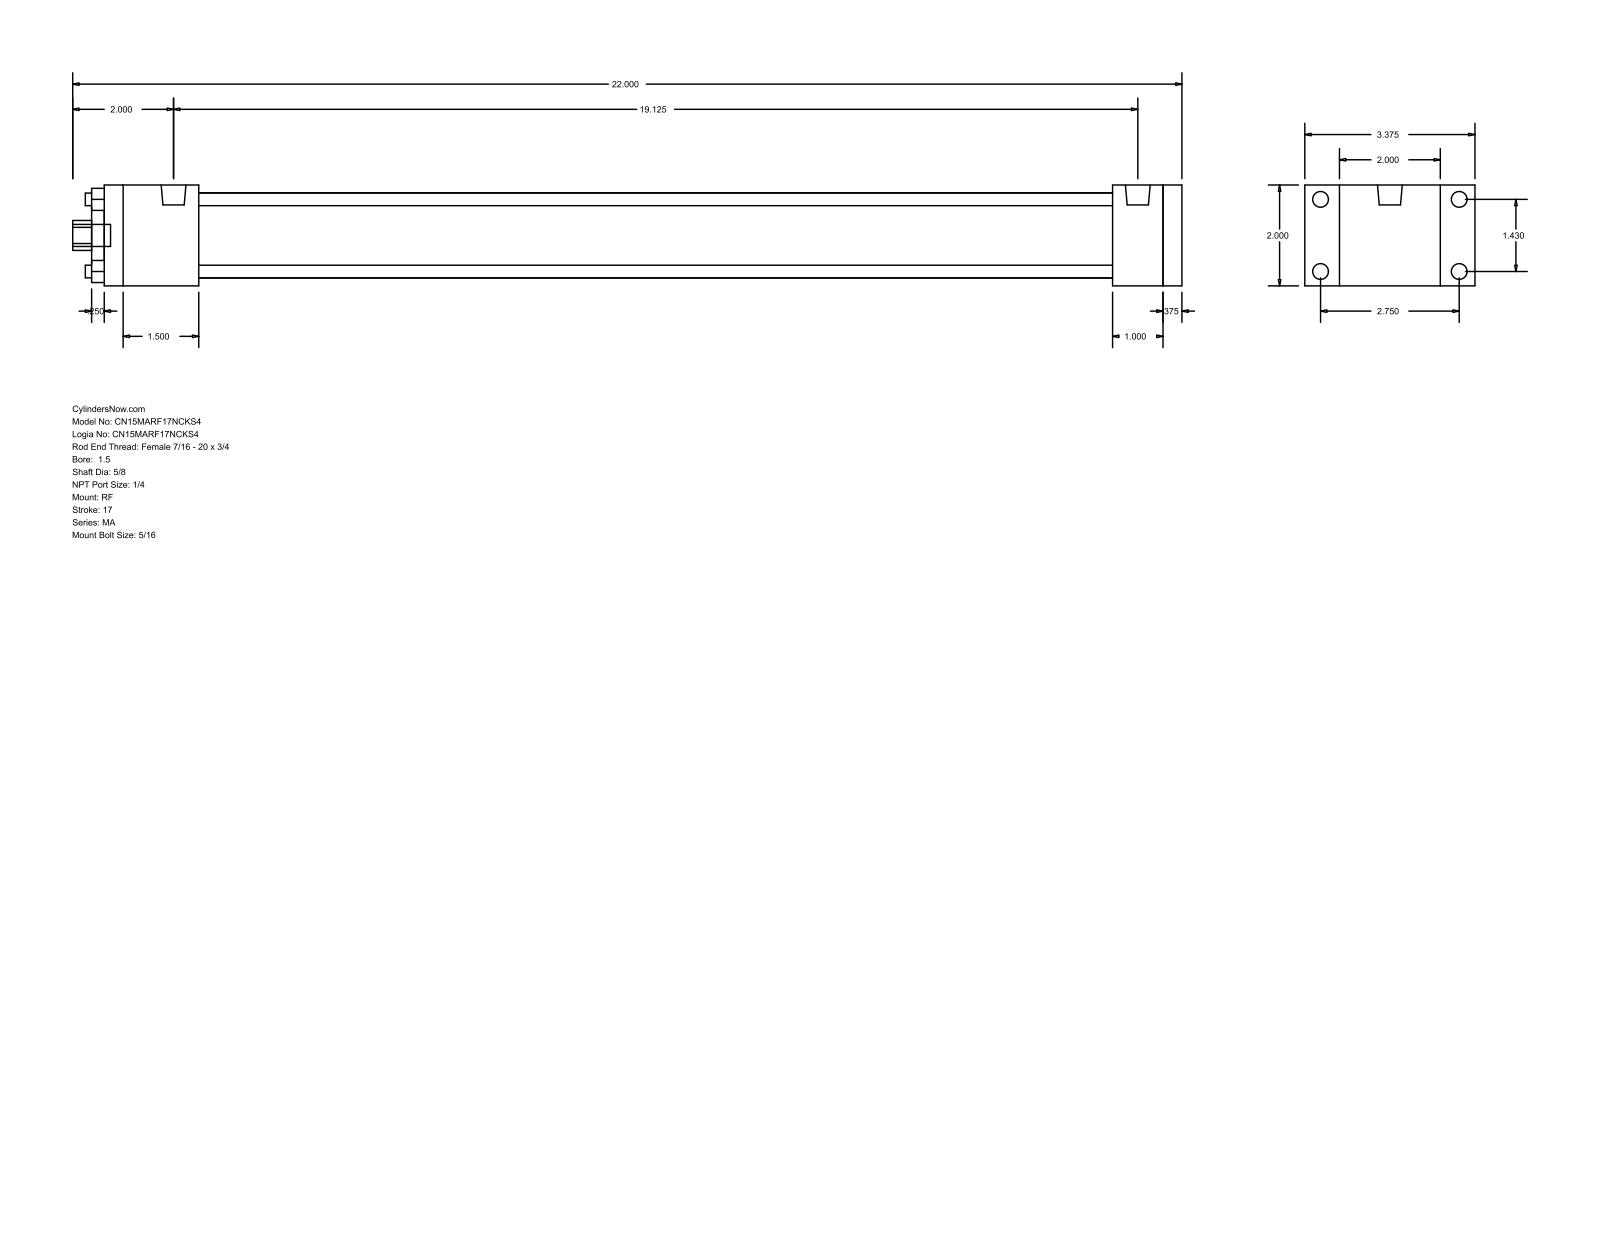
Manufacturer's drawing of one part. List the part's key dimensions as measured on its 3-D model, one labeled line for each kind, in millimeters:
Part name (STEP PRODUCT): MA_RF__0150_0.625
STEP written by: GSSL Pune (CONFIG_CONTROL_DESIGN)
Units: millimetres
Bodies: 0 solids, 92 faces (64 planar, 28 cylindrical, 0 other)
Overall size (bounding box): 558.8 × 85.72 × 50.8
Round holes (diameter × count): ⌀6.35 ×4, ⌀15.88 ×1, ⌀28.57 ×1, ⌀42.93 ×1
Round bosses / shafts (diameter × count): ⌀7.94 ×8, ⌀12.49 ×2, ⌀11.11 ×1
Partial cylindrical surfaces — rounded edges, fillets, slot ends (radius × count): R7.54 ×1
Main face-to-face distances: 50.8, 9.53, 542.92, 533.39, 508, 25.39, 34.92, 47.62, 460.38, 485.77
Hole centre spacings: 25.68, 36.32, 51.36
